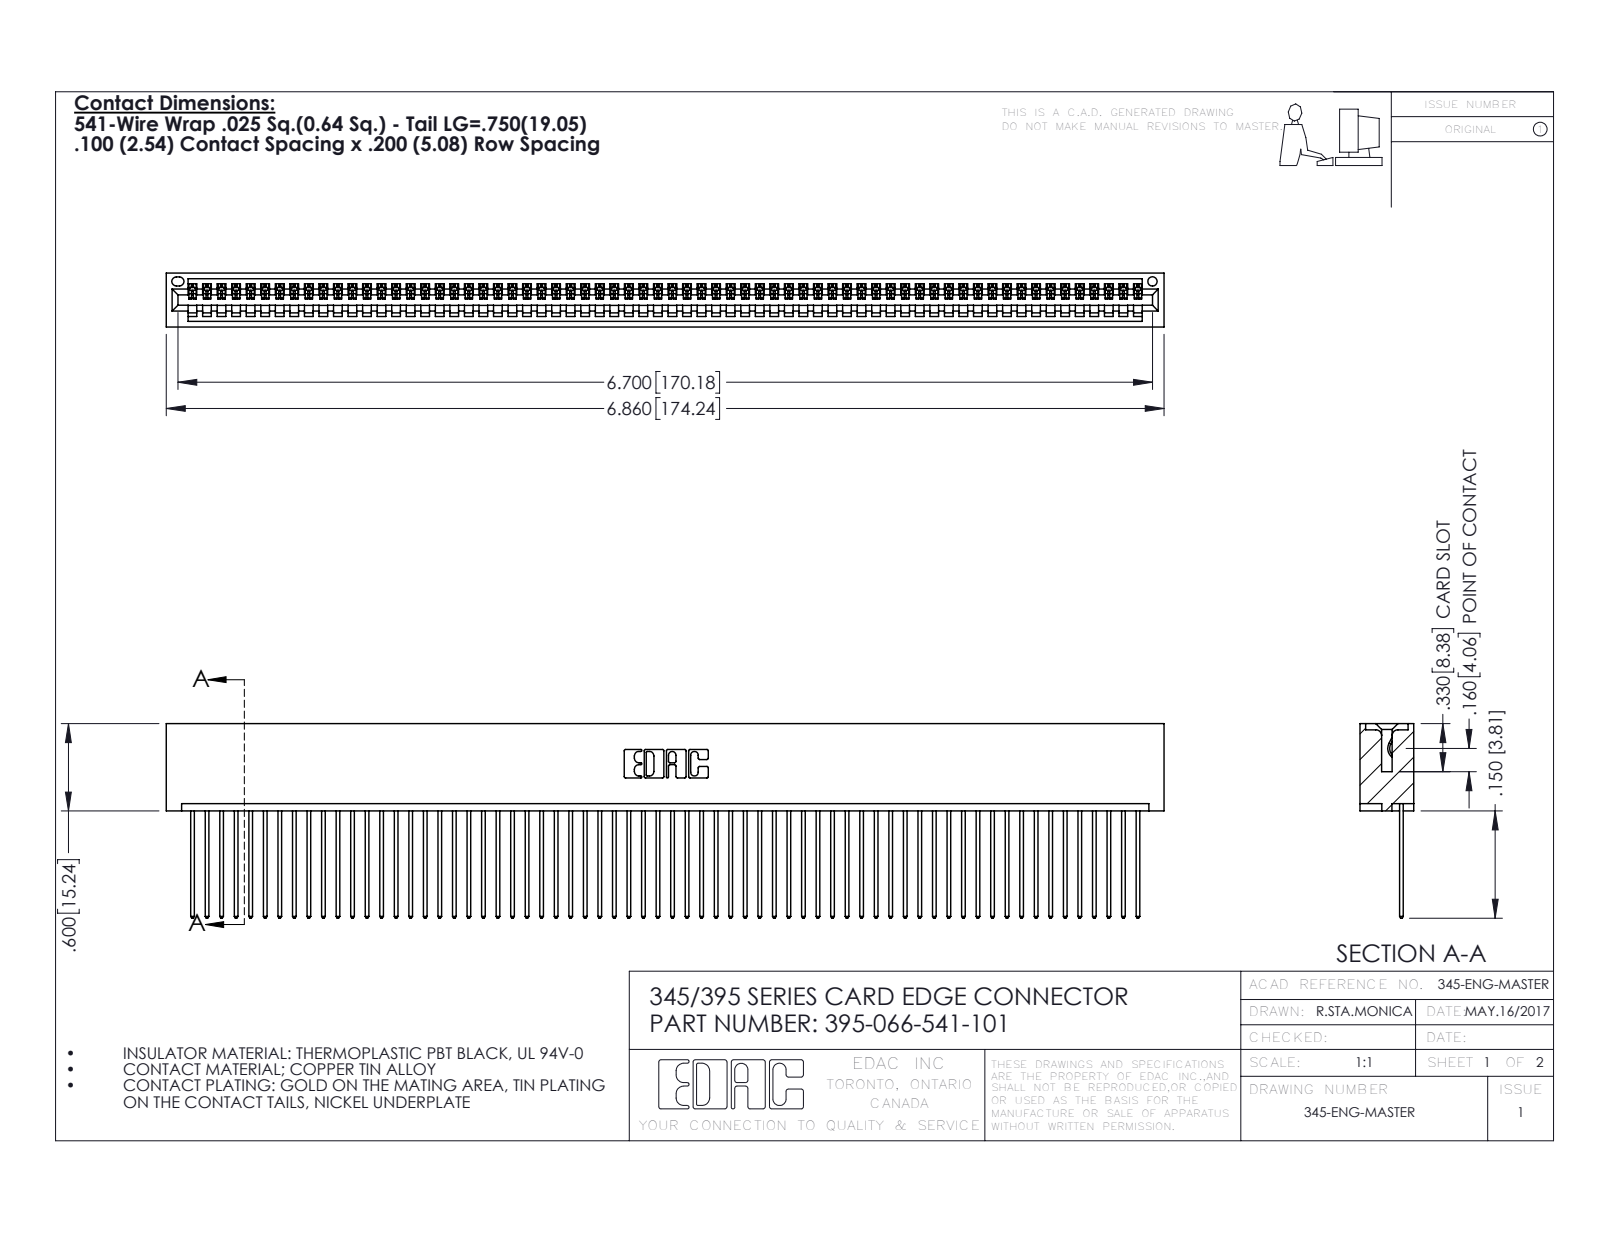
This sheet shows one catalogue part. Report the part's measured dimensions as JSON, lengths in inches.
{"part_name": "395-066-541-101; 345-292-001_345-293-141; 345 Part_No Mounting Lugs", "step_written_by": "SolidWorks 2016 (CONFIG_CONTROL_DESIGN)", "units": "inches", "bodies": {"solids": 67, "faces": 3946, "planar": 2716, "cylindrical": 1230, "other": 0}, "overall_size": [6.86, 1.337, 0.37], "volume_in3": 1.071, "surface_area_in2": 38.93, "round_holes": [[0.064, 1]], "partial_cylinders_radius": [[0.006, 132], [0.01, 132], [0.01, 22], [0.007, 6], [0.031, 6], [0.026, 3], [0.031, 2], [0.04, 2]], "face_to_face_distances": [0.072, 0.298, 0.098, 0.272, 0.025, 0.37, 0.2, 0.225, 0.149, 0.072]}
